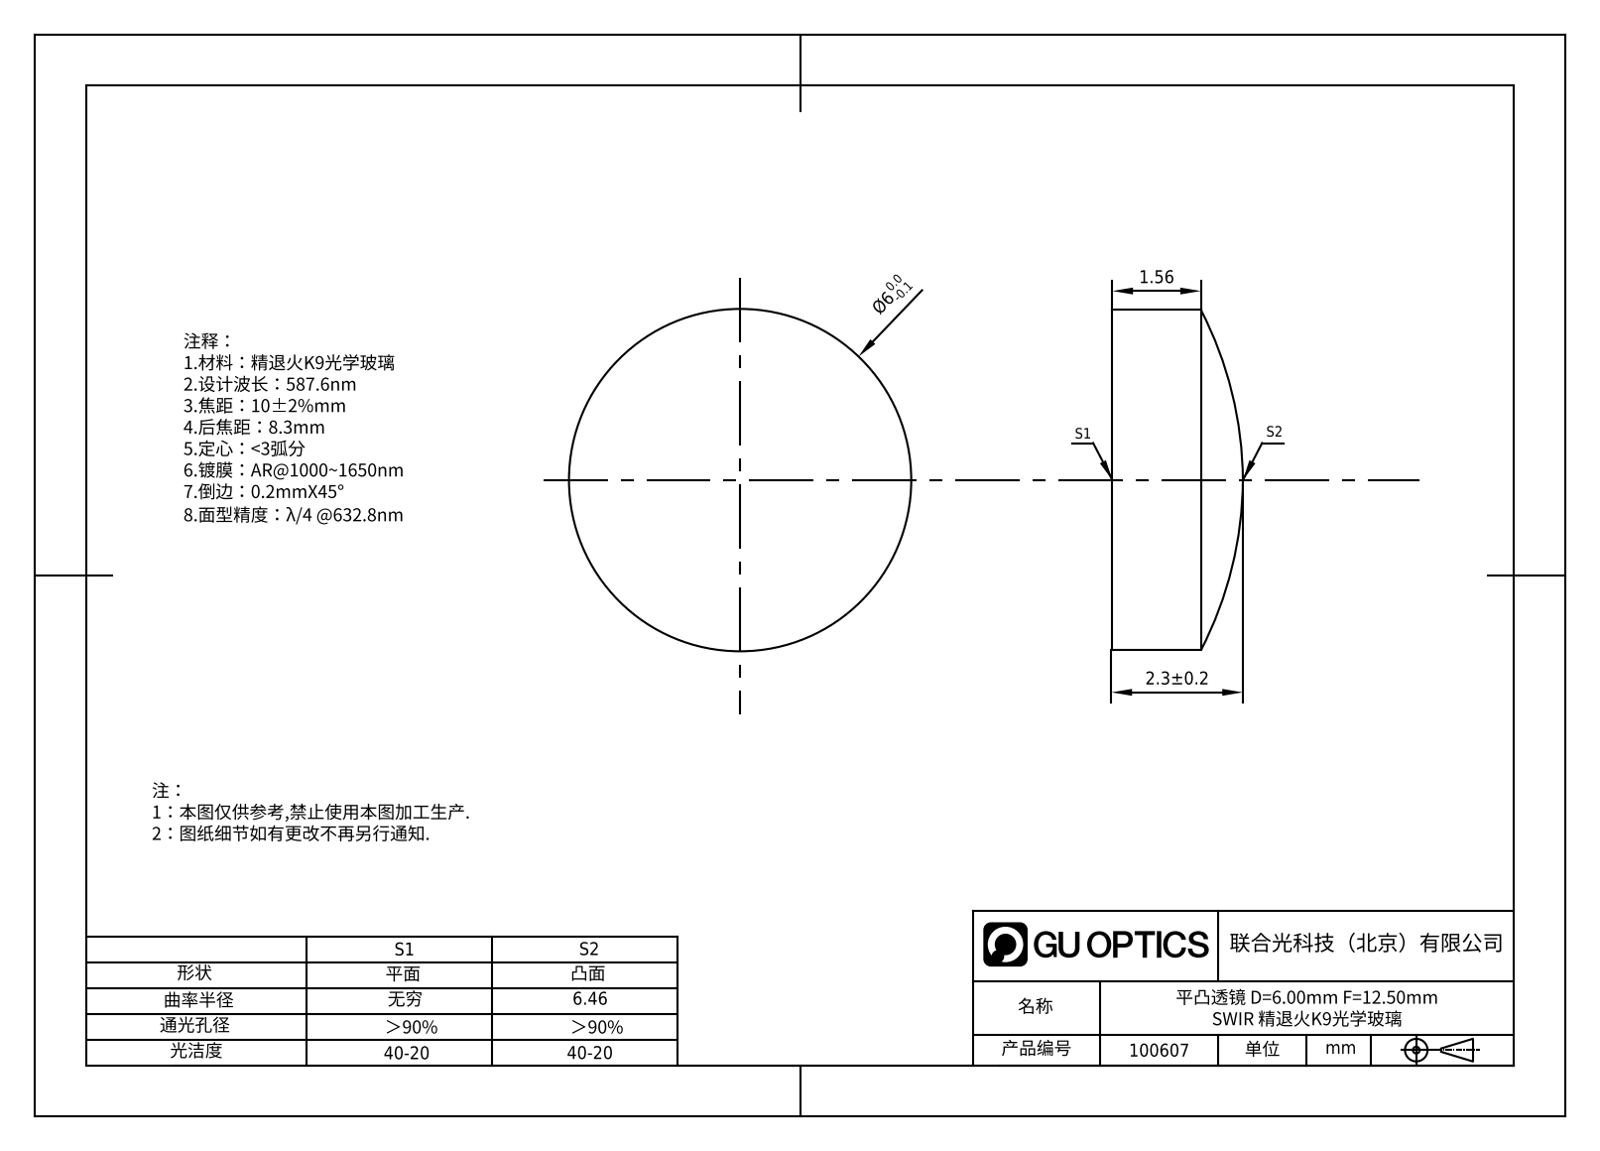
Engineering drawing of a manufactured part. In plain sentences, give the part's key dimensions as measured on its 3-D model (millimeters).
The part is named "100584". Its 3-D file was written by "SolidWorks 2020 (CONFIG_CONTROL_DESIGN)". It is 1 solid with 5 faces: 1 planar, 2 cylindrical and 2 other. Overall it measures 6 by 6 by 2.3 millimeters. Its volume is 55 cubic millimeters and its surface area 88 square millimeters. Round bosses or shafts: 1 of diameter 6.
